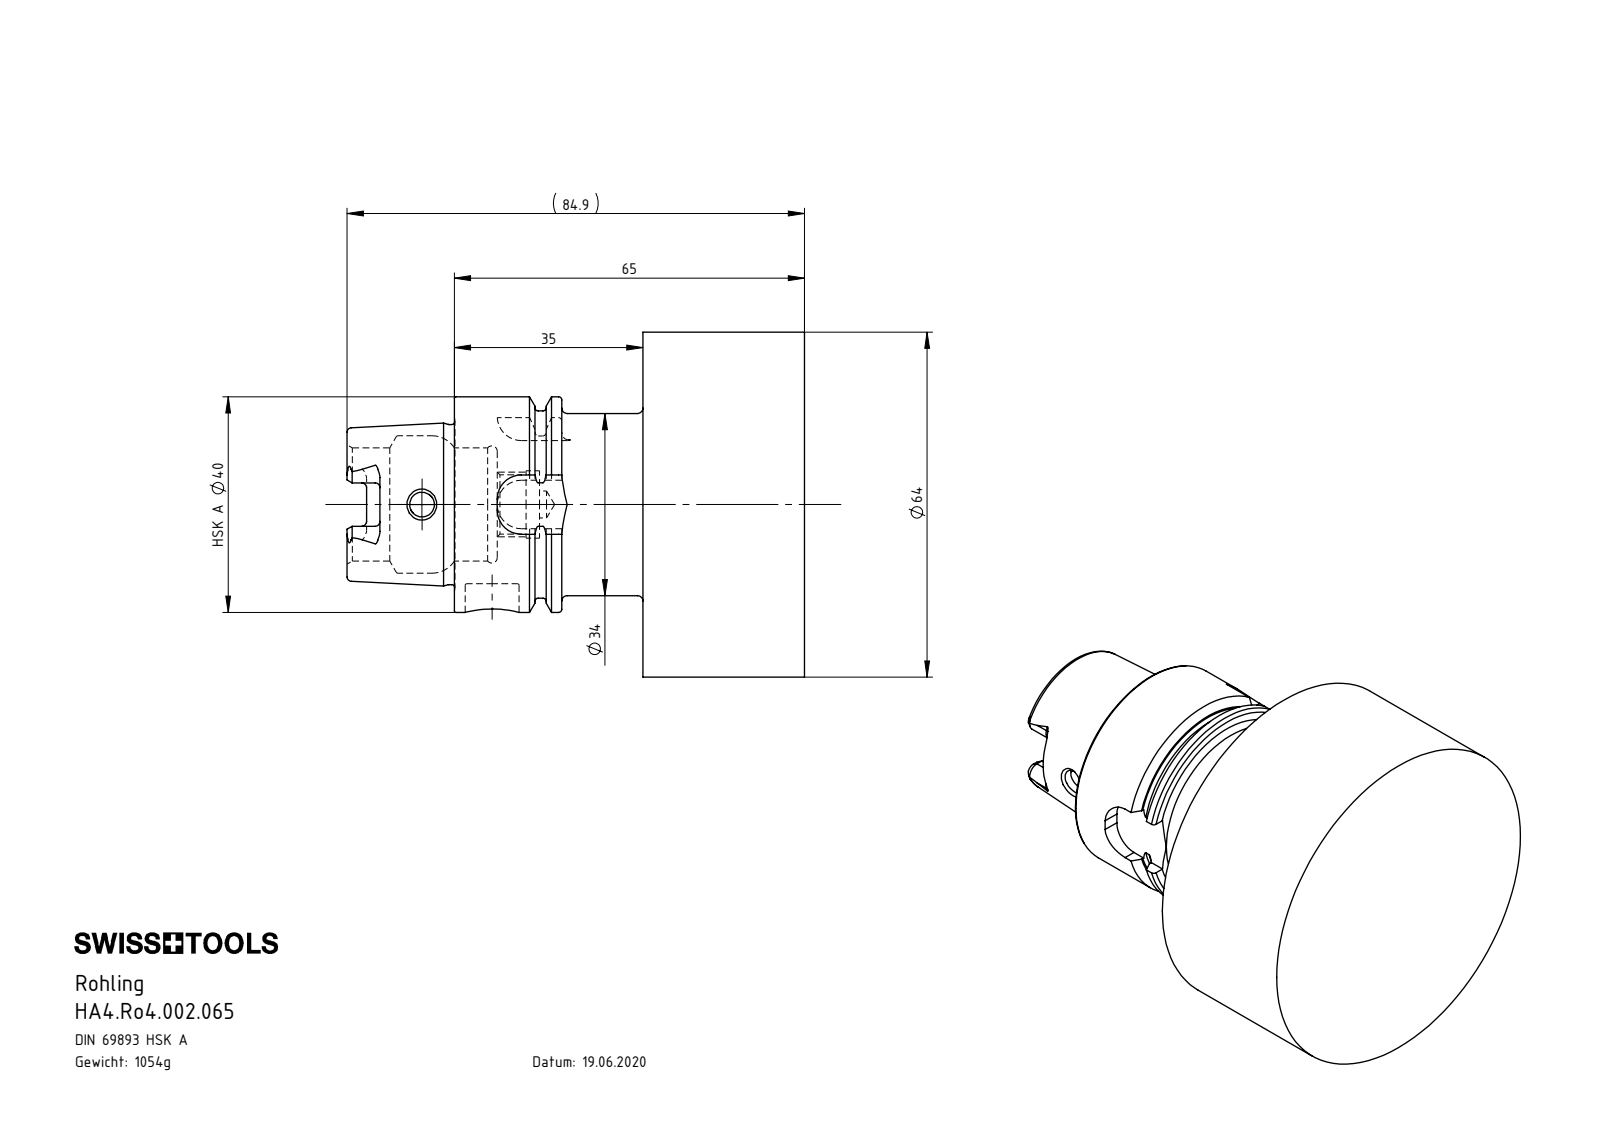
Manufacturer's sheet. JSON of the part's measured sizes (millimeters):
{"part_name": "HA4.Ro4.002.065", "step_written_by": "SolidWorks 2022 (AUTOMOTIVE_DESIGN)", "units": "millimeters", "bodies": {"solids": 1, "faces": 173, "planar": 48, "cylindrical": 53, "other": 72}, "overall_size": [88.9, 64, 64], "volume_mm3": 134266, "surface_area_mm2": 21823, "round_holes": [[1.6, 1], [4.6, 1], [5, 1], [10, 1], [11, 1], [12.5, 1], [21, 1], [25.5, 1]], "round_bosses_or_shafts": [[64, 1], [40, 1], [34.75, 1], [33.8, 1], [29.71, 1], [6, 1]], "partial_cylinders_radius": [[0.9, 6], [1.88, 4], [4.5, 4], [4.02, 1]], "face_to_face_distances": [30, 35, 65, 7.95, 27.05, 57.05, 19.95, 12, 15.05, 45.05]}
